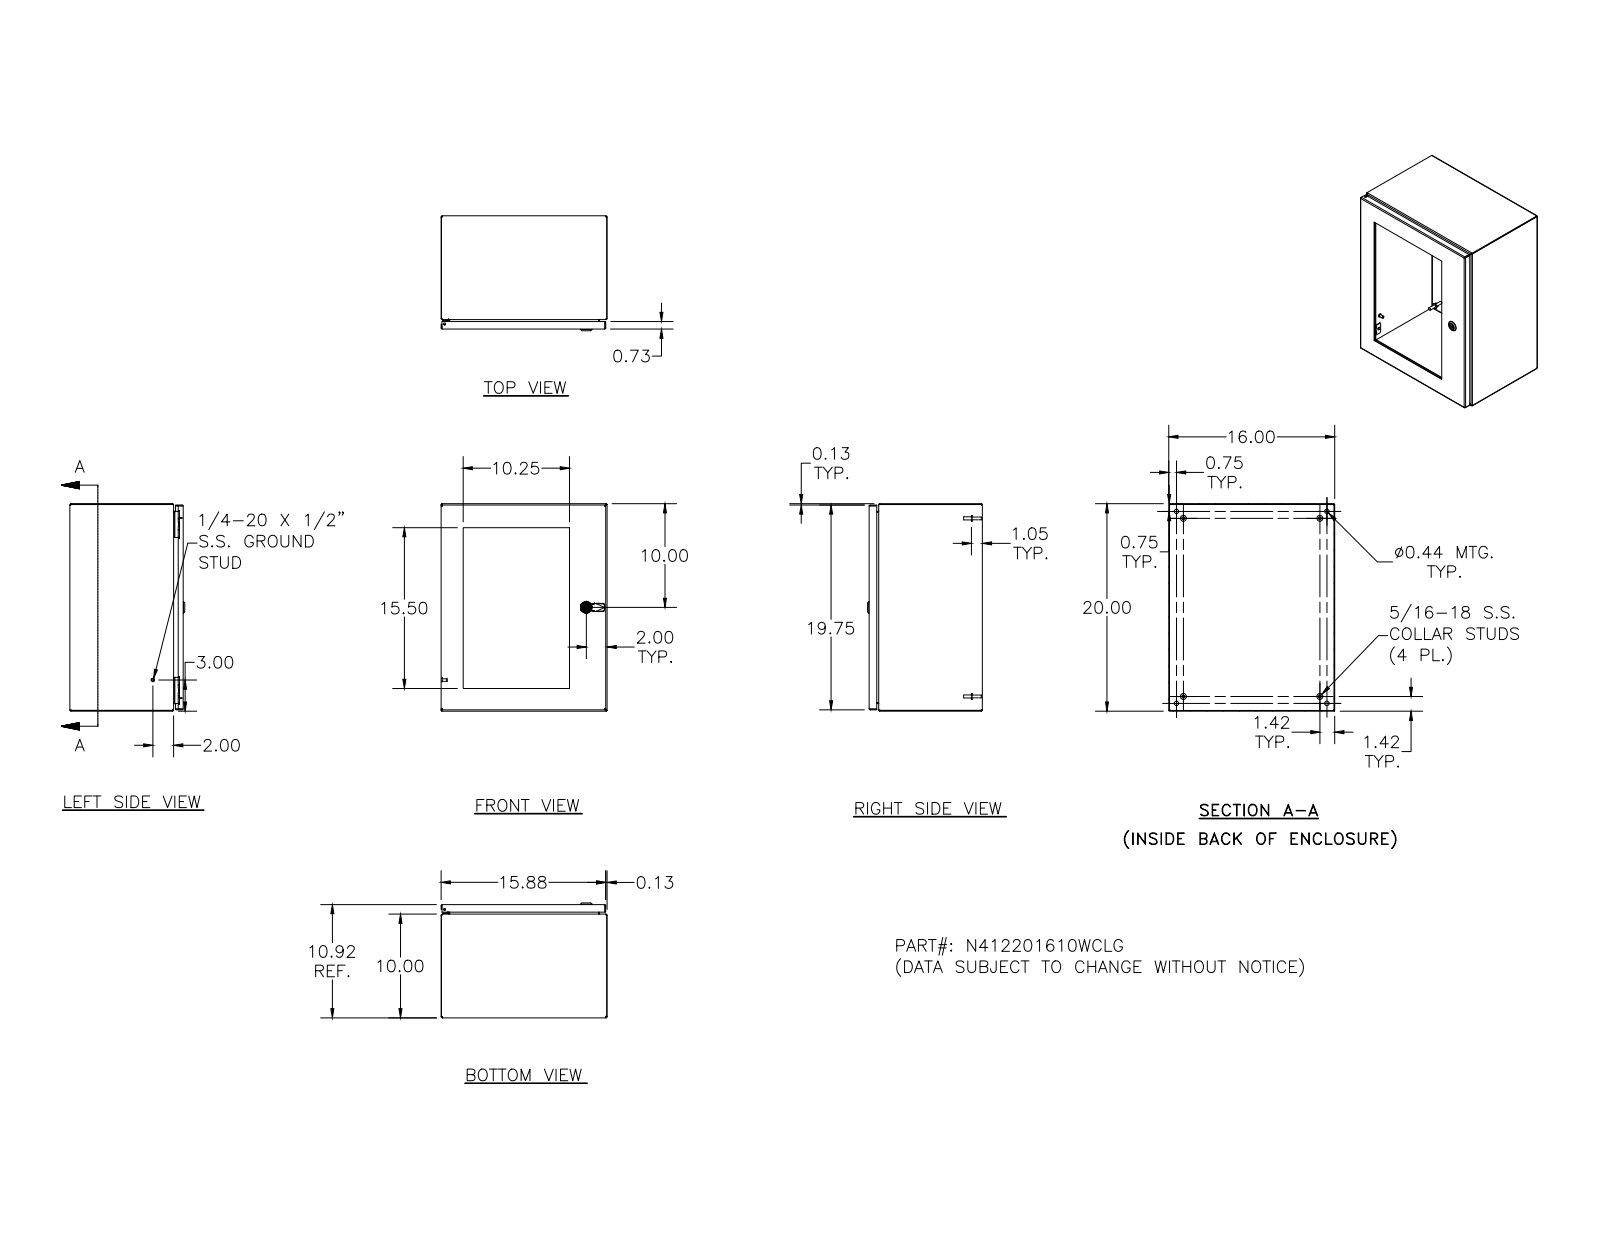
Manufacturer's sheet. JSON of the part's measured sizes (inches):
{"part_name": "N412201610WCLG", "step_written_by": "SolidWorks 2018 (AUTOMOTIVE_DESIGN)", "units": "inches", "bodies": {"solids": 65, "faces": 1955, "planar": 731, "cylindrical": 609, "other": 615}, "overall_size": [20, 16, 11.075], "volume_in3": 150.9, "surface_area_in2": 3244, "round_holes": [[0.156, 16], [0.281, 14], [0.188, 5], [0.093, 4], [0.152, 4], [0.167, 4], [0.172, 4], [0.437, 4], [0.187, 1], [0.197, 1], [0.315, 1], [0.394, 1]], "round_bosses_or_shafts": [[0.337, 14], [0.19, 14], [0.25, 10], [0.563, 4], [0.36, 4], [0.32, 4], [0.3, 4], [0.275, 4]], "partial_cylinders_radius": [[0.031, 34], [0.012, 30], [0.05, 26], [0.105, 24], [0.016, 18], [0.125, 16], [0.02, 13], [0.032, 8]], "face_to_face_distances": [0.074, 10.843, 15.926, 10.769, 19.926, 16, 15.852, 0.25, 10.593, 10.519], "hole_center_spacings": [4, 8, 12.176, 16, 6.221, 8.585, 10.035, 11.5]}
